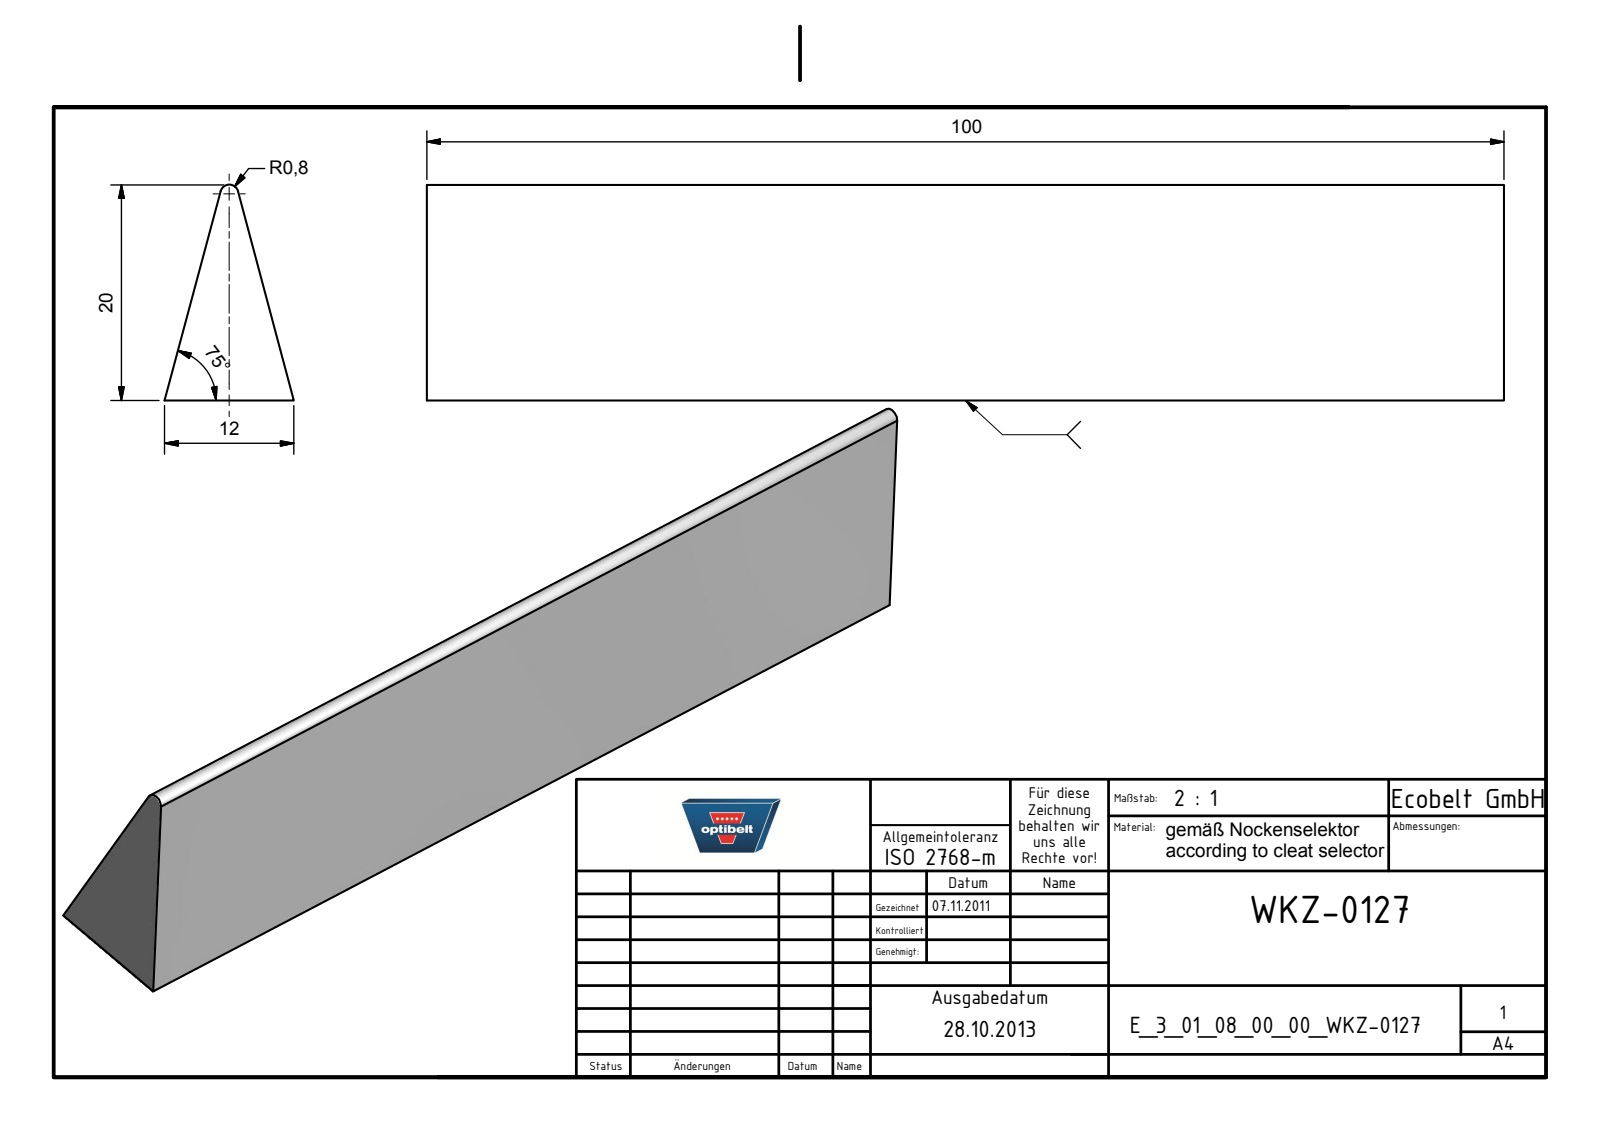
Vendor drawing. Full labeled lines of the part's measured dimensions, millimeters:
Part name (STEP PRODUCT): E_3_01_08_00_00_WKZ-0127
STEP written by: Autodesk Inventor 2025 (AUTOMOTIVE_DESIGN)
Units: millimetres
Bodies: 1 solid, 6 faces (5 planar, 1 cylindrical, 0 other)
Overall size (bounding box): 100 × 20 × 12
Volume: 13 266 mm³ · Surface area: 5 697 mm²
Partial cylindrical surfaces — rounded edges, fillets, slot ends (radius × count): R0.83 ×1
Main face-to-face distances: 100
